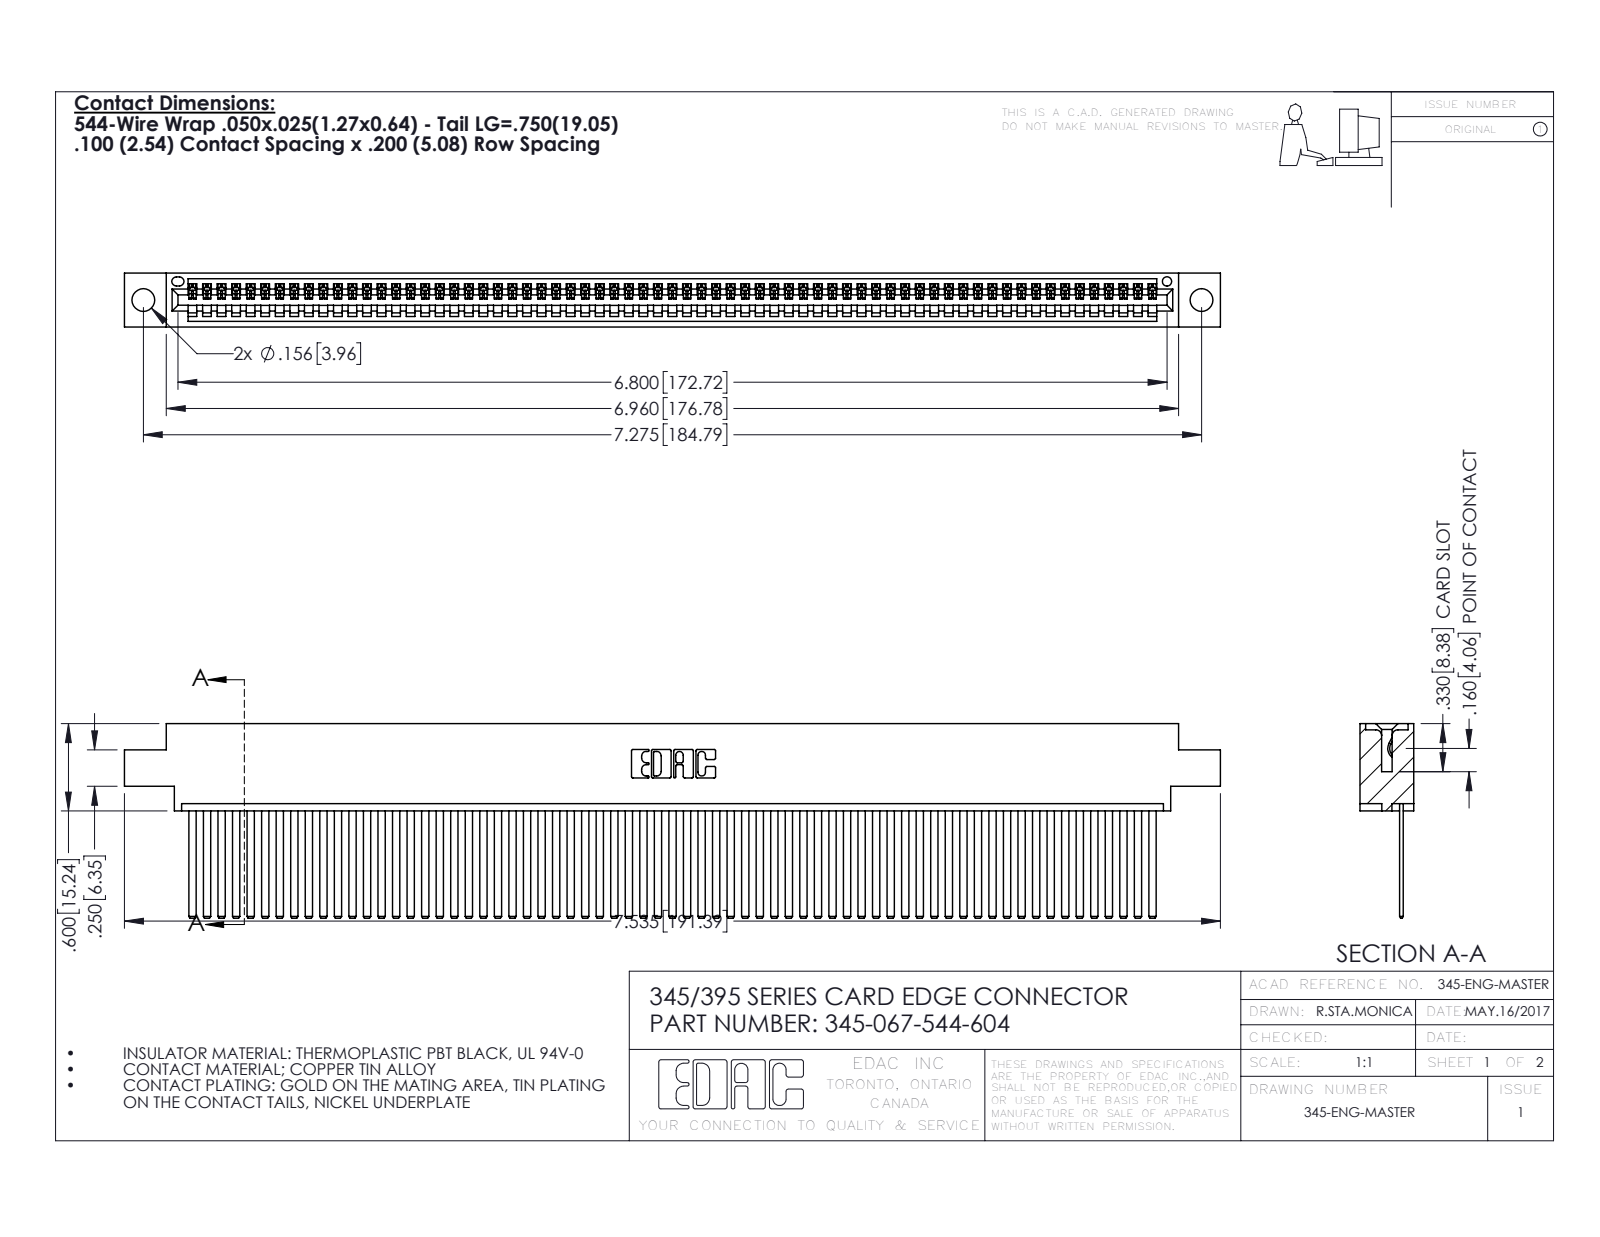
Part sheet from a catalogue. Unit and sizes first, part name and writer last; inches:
Units: inches
Overall size (bounding box): 7.535 × 1.337 × 0.37
Round holes (diameter × count): ⌀0.156 ×2, ⌀0.064 ×1
Partial cylindrical surfaces — rounded edges, fillets, slot ends (radius × count): R0.006 ×134, R0.01 ×22, R0.007 ×6, R0.031 ×6, R0.026 ×3, R0.031 ×2, R0.04 ×2, R0.014 ×1
Main face-to-face distances: 0.072, 0.298, 0.025, 0.098, 0.272, 0.37, 0.2, 0.225, 0.175, 0.149
Hole centre spacings: 0.27, 7.039, 7.275
Volume: 1.157 in³ · Surface area: 43.09 in²
Bodies: 68 solids, 3614 faces (2496 planar, 1118 cylindrical, 0 other)
Part name (STEP PRODUCT): 345-292-001_345-293-144; 345-067-544-604; 345 Part_0.170 Offset - 0.156 Dia-TH
STEP written by: SolidWorks 2016 (CONFIG_CONTROL_DESIGN)
